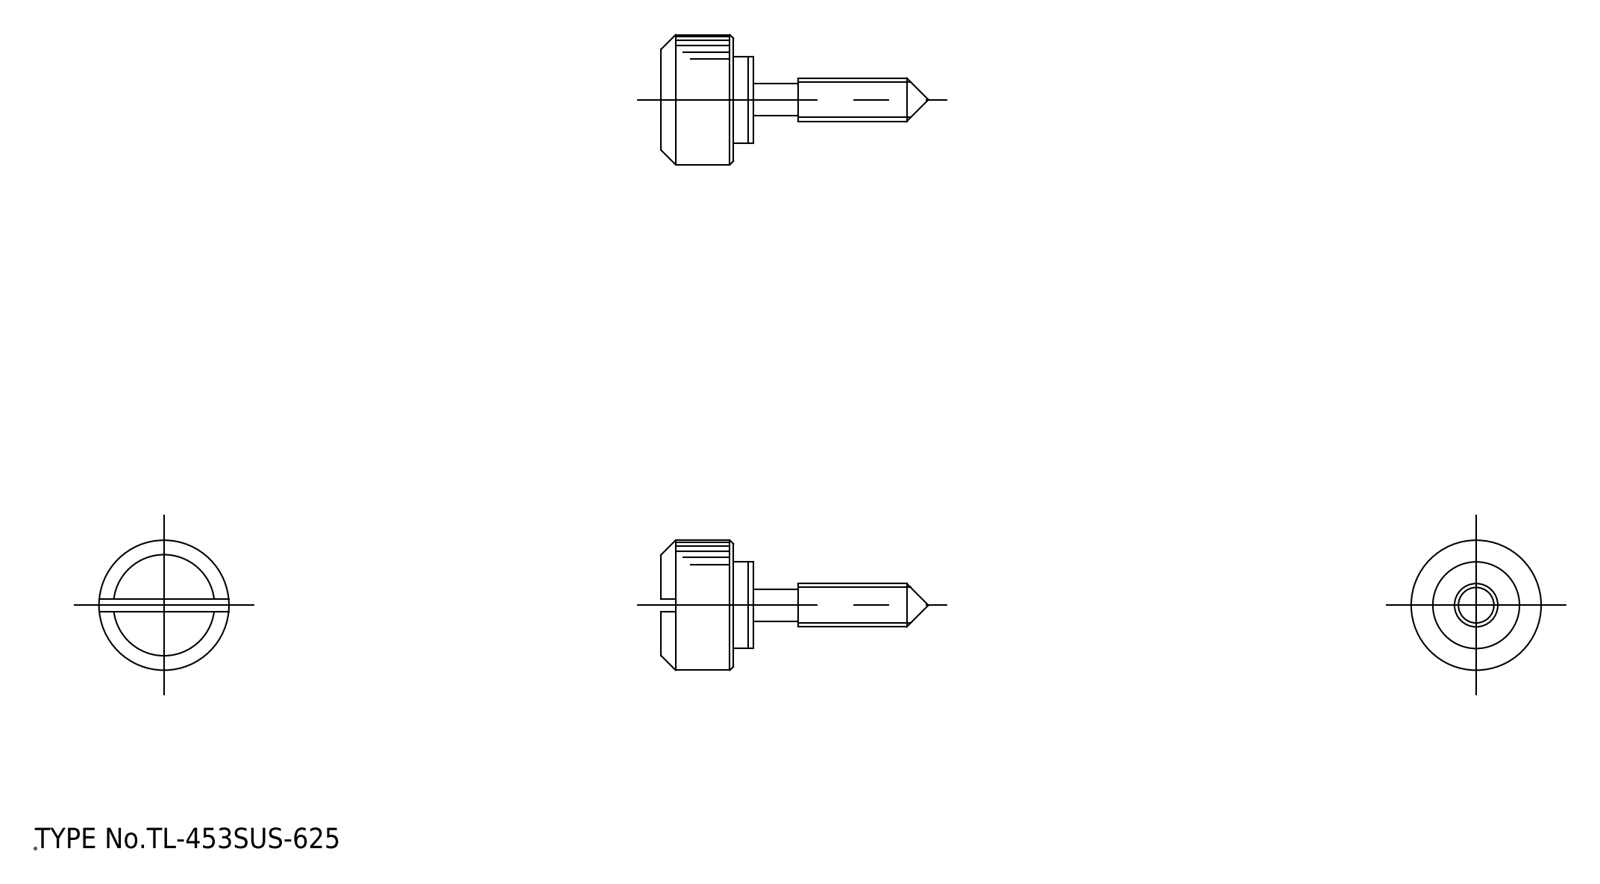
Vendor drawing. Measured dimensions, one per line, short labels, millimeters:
name: washer; knob
written by: spGate 19.8.4 (****-****-****-****) (AUTOMOTIVE_DESIGN)
unit: mm
bodies: 2 solids, 42 faces (18 planar, 18 cylindrical, 6 other)
size: 37 × 18 × 18
volume: 3 235 mm³; area: 1 760 mm²
bosses: 1× ⌀18, 1× ⌀12, 1× ⌀6, 1× ⌀4.5
rounds: 4× R1, 1× R2.3
face distances: 2, 10, 12, 12.8, 2.8, 0.8, 8, 10.8, 1.8, 19
